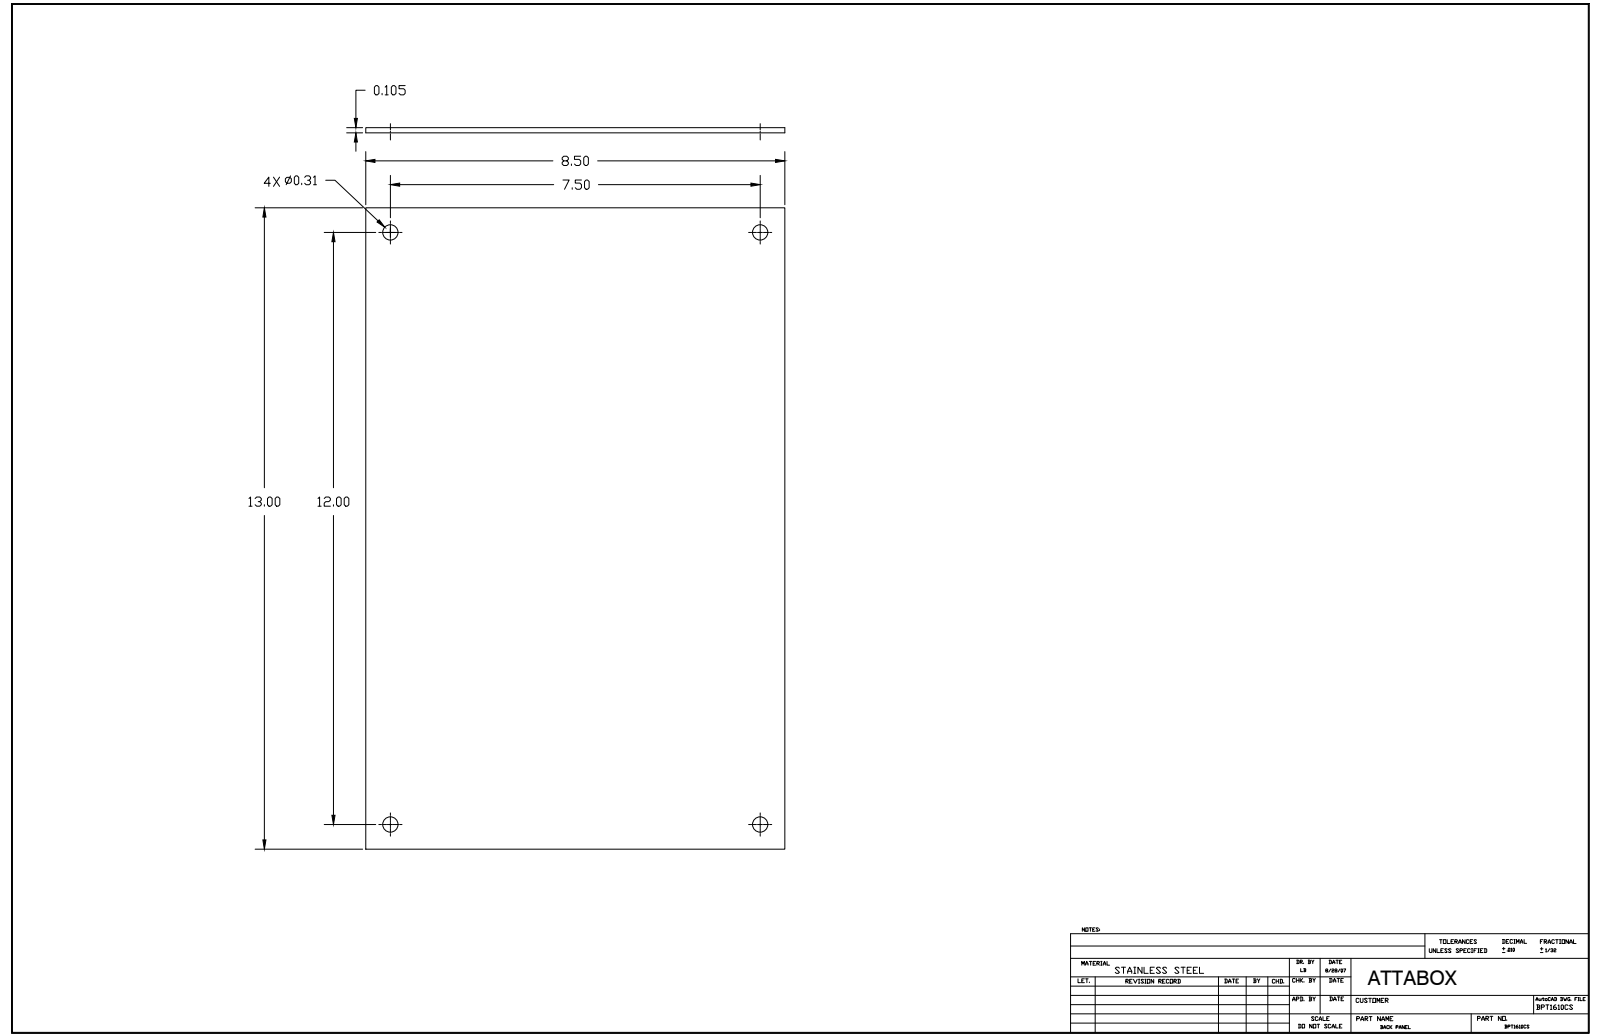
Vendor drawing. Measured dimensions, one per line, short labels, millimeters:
name: BP1610CS_STP
written by: Autodesk Inventor 2014 (AUTOMOTIVE_DESIGN)
unit: mm
bodies: 1 solid, 10 faces (6 planar, 4 cylindrical, 0 other)
size: 330.2 × 215.9 × 2.67
volume: 189 611 mm³; area: 145 368 mm²
holes: 4× ⌀7.87
face distances: 2.66, 215.9, 330.2
hole spacings: 190.5, 304.8, 359.43
